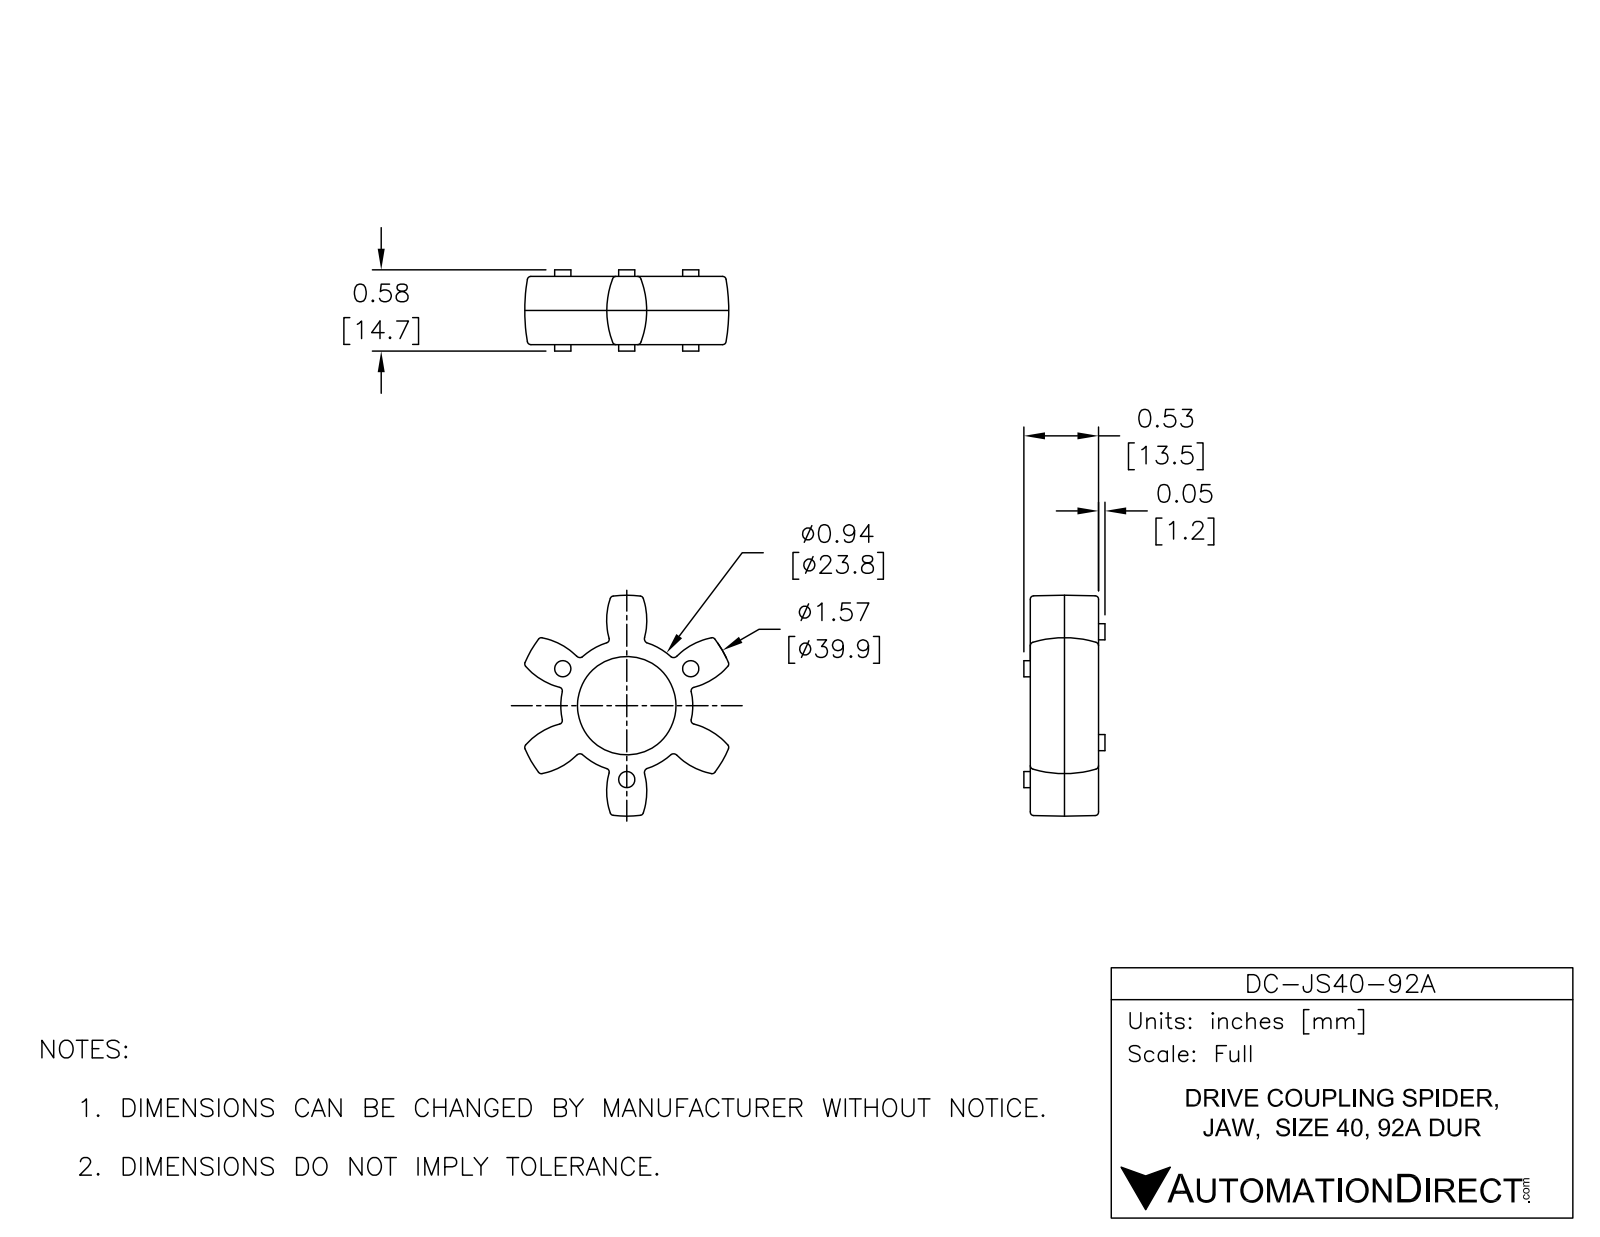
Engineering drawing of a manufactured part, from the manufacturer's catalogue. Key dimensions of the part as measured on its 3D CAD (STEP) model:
Part name (STEP PRODUCT): DC-JS40-92A
STEP written by: SolidWorks 2015 (AUTOMOTIVE_DESIGN)
Units: millimetres
Bodies: 1 solid, 218 faces (8 planar, 14 cylindrical, 196 other)
Overall size (bounding box): 39.88 × 36.86 × 14.66
Volume: 6 394 mm³ · Surface area: 3 734 mm²
Round holes (diameter × count): ⌀17.78 ×1
Round bosses / shafts (diameter × count): ⌀2.92 ×6
Main face-to-face distances: 12.32, 1.17, 13.49, 14.66
